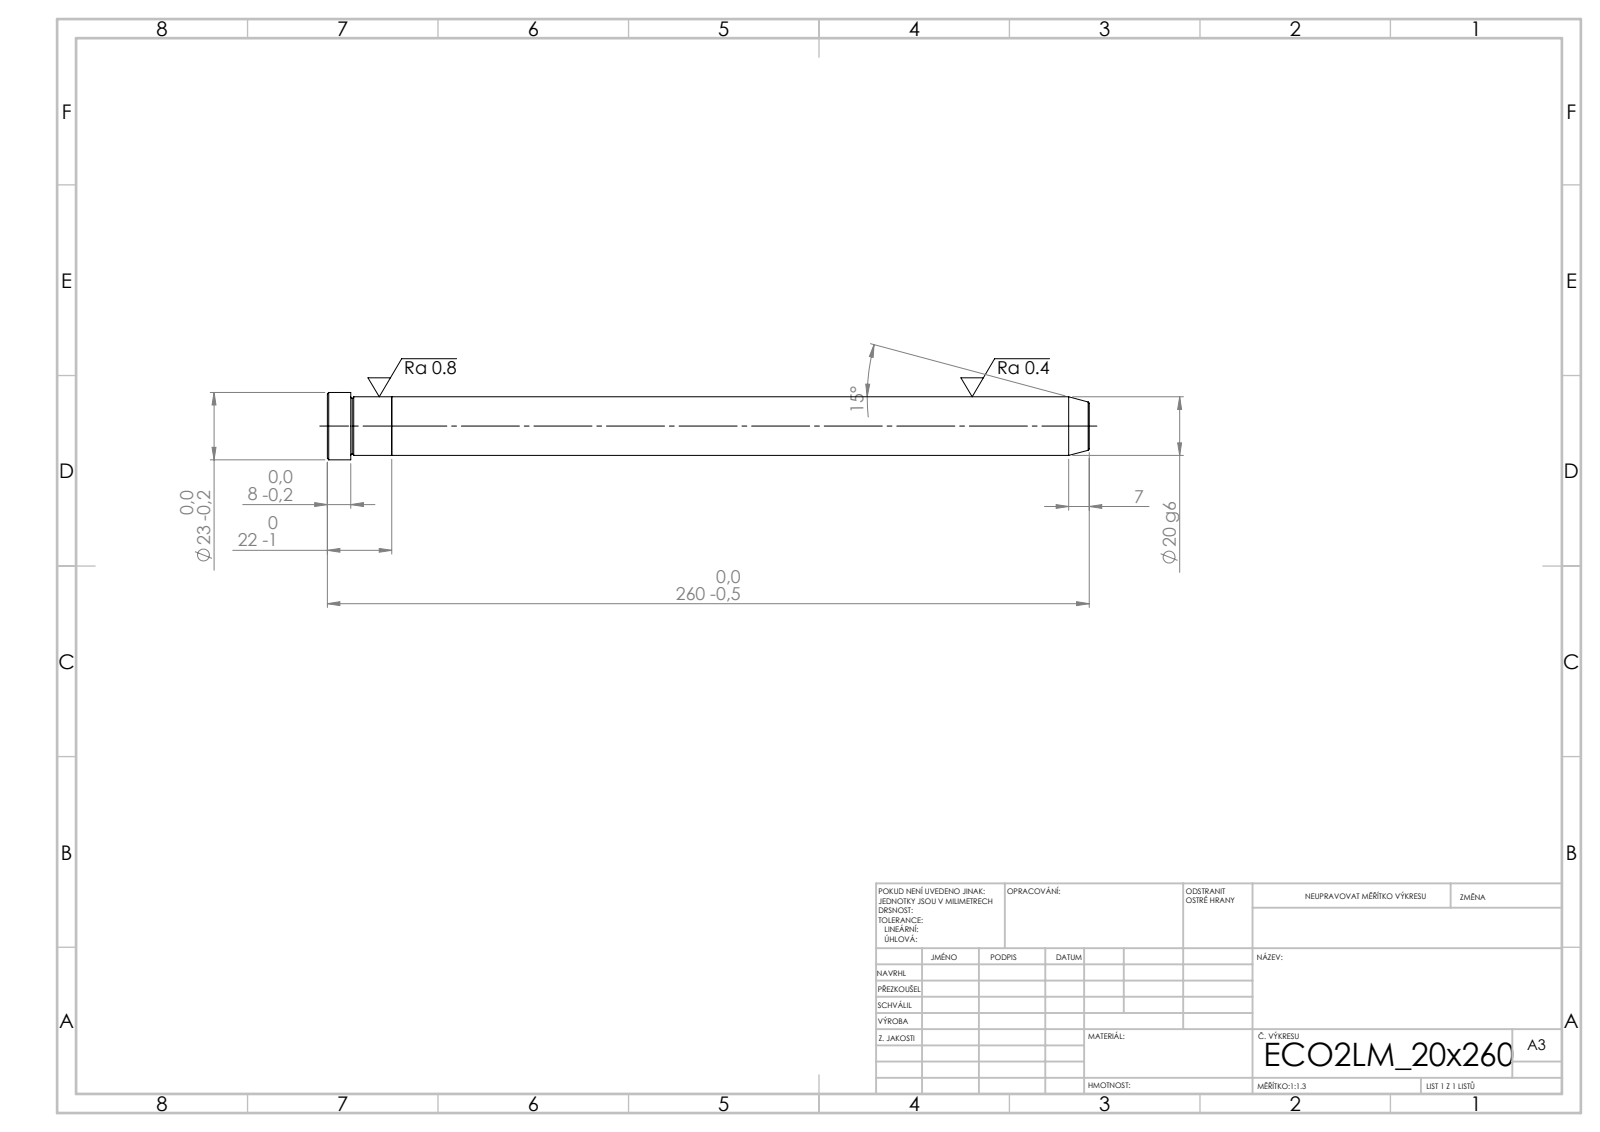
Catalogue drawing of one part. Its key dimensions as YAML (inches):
step_written_by: "SolidWorks 2019 (CONFIG_CONTROL_DESIGN)"
units: inches
bodies: {solids: 2, faces: 21, planar: 5, cylindrical: 6, other: 10}
overall_size: [10.236, 0.906, 0.906]
volume: 5.008
surface_area: 27.5
round_bosses_or_shafts:
  - {diameter: 0.906, count: 1}
  - {diameter: 0.787, count: 1}
face_to_face_distances: [0.866, 9.37, 10.236, 9.921, 0.551, 0.315]
